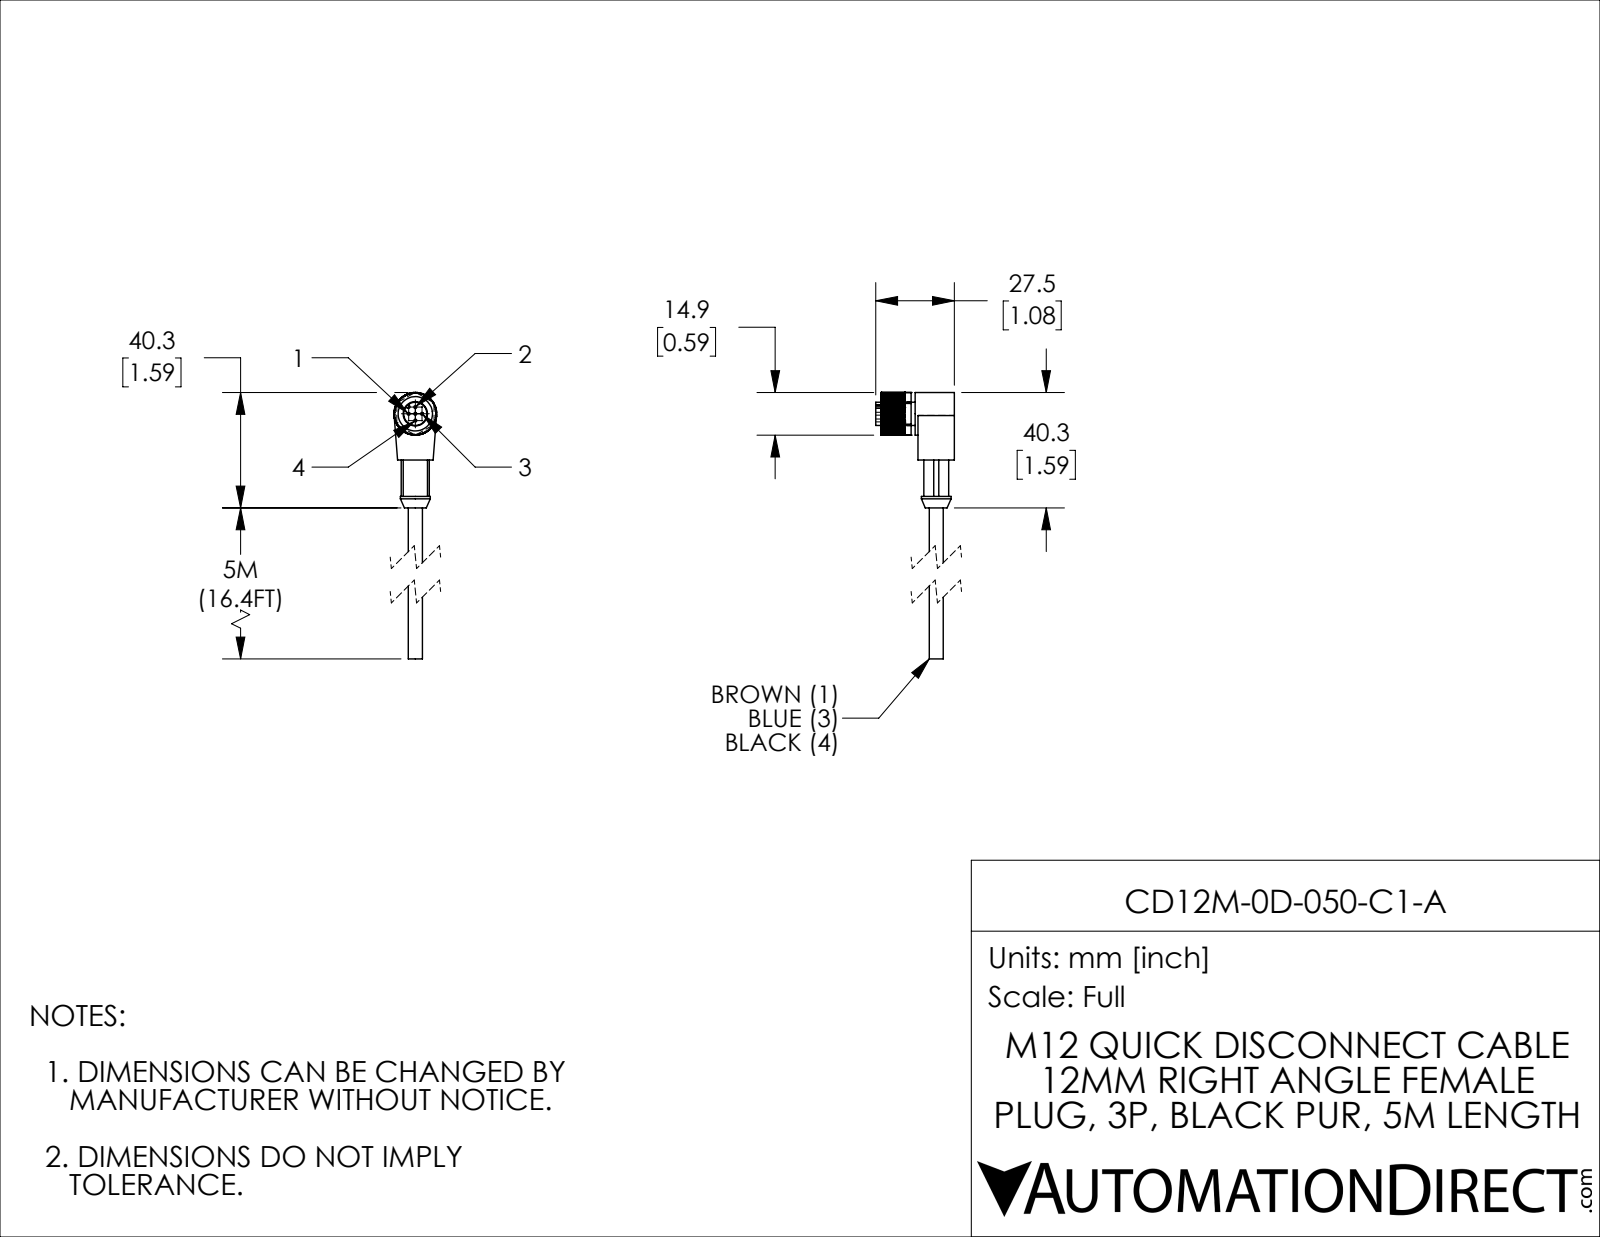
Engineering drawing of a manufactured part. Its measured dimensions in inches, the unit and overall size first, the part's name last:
Units: inches
Overall size (bounding box): 5.524 × 1.083 × 0.587
Round holes (diameter × count): ⌀0.039 ×5, ⌀0.335 ×1, ⌀0.472 ×1
Round bosses / shafts (diameter × count): ⌀0.587 ×1, ⌀0.409 ×1, ⌀0.343 ×1, ⌀0.319 ×1, ⌀0.193 ×1
Partial cylindrical surfaces — rounded edges, fillets, slot ends (radius × count): R0.022 ×1
Main face-to-face distances: 0.539, 0.5, 0.039, 0.055, 0.594, 0.094, 0.657, 0.232, 1.008, 0.508
Hole centre spacings: 0.093, 0.131, 0.185
Volume: 0.52 in³ · Surface area: 8.518 in²
Bodies: 4 solids, 326 faces (218 planar, 106 cylindrical, 2 other)
Part name (STEP PRODUCT): CD12M-0D-050-C1-A
STEP written by: SolidWorks 2021 (CONFIG_CONTROL_DESIGN)
